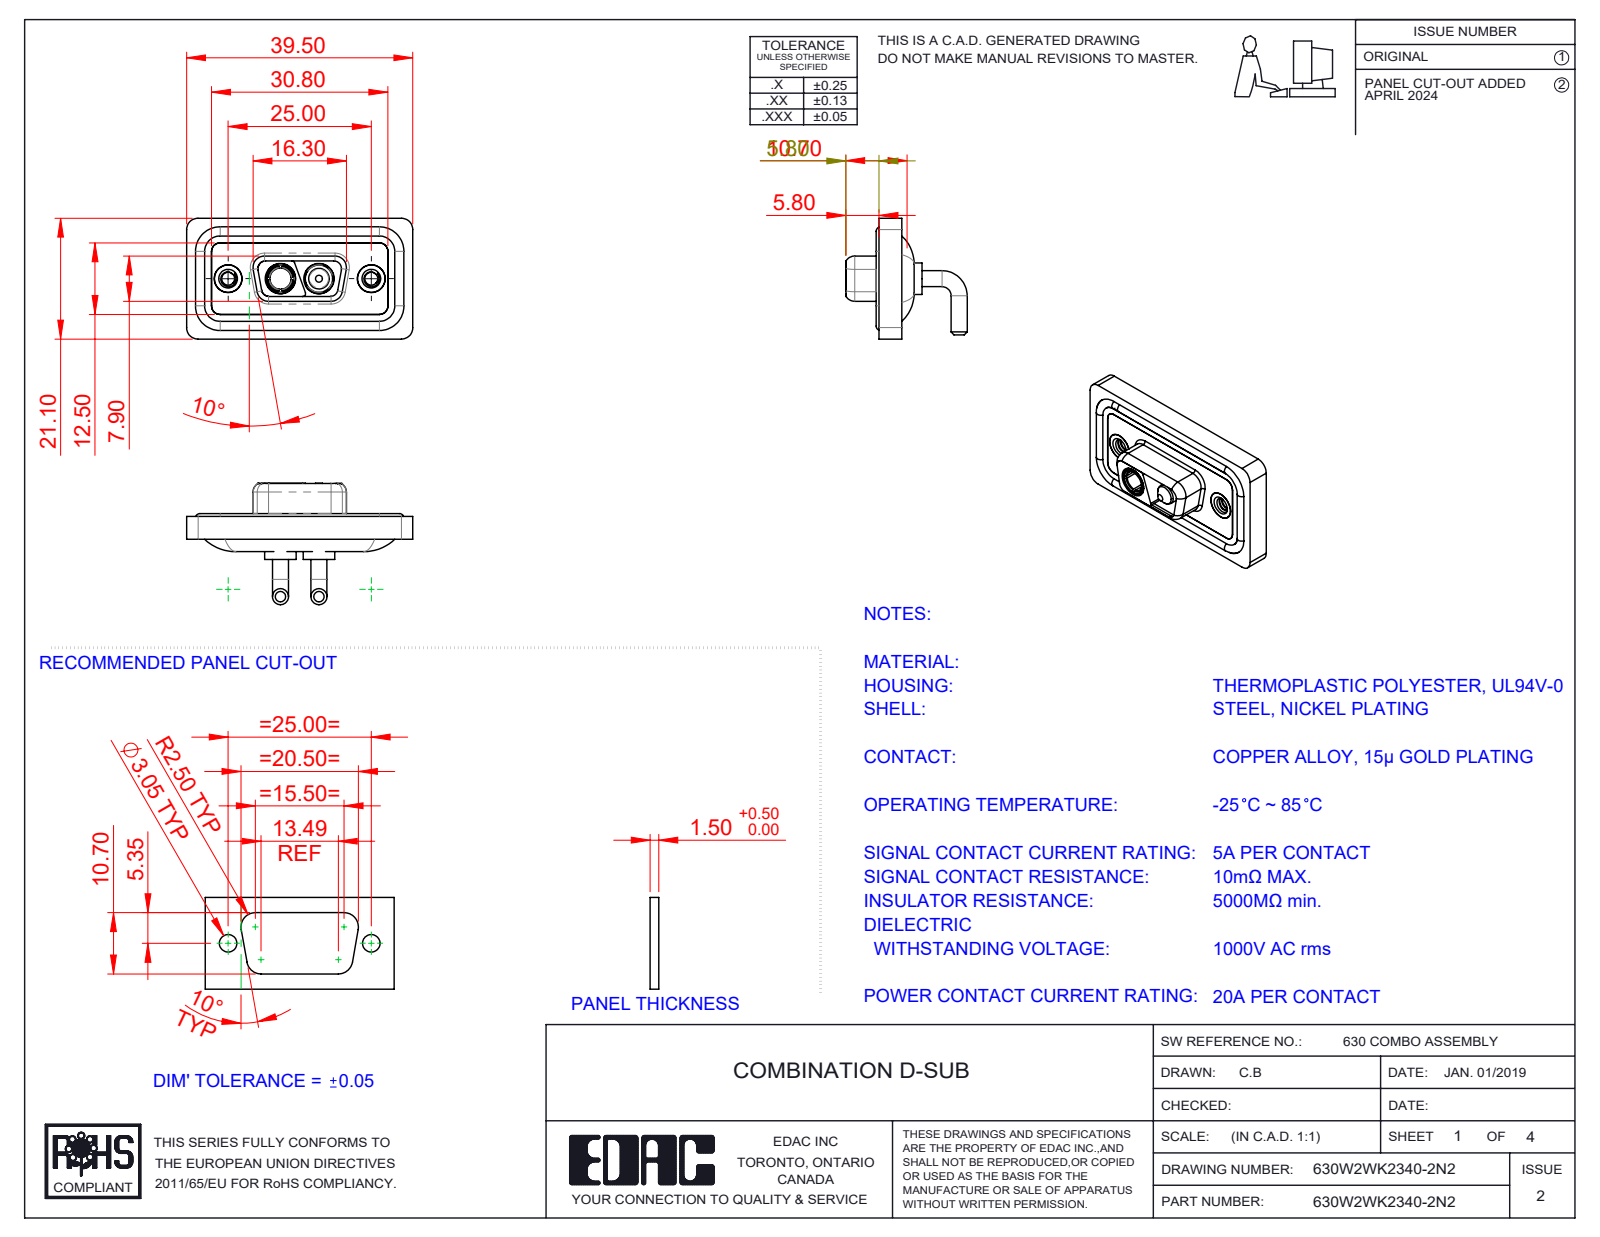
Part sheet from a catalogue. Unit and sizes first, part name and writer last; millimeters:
Units: millimetres
Overall size (bounding box): 39.5 × 21.2 × 21.1
Round holes (diameter × count): ⌀4.85 ×4, ⌀2.26 ×2, ⌀4 ×2, ⌀4.05 ×2, ⌀5 ×2, ⌀5.3 ×2, ⌀3.7 ×1
Round bosses / shafts (diameter × count): ⌀2.8 ×4, ⌀1.6 ×4, ⌀5.5 ×2, ⌀5.2 ×2, ⌀4.95 ×2, ⌀4.8 ×2, ⌀4.75 ×2, ⌀3.75 ×2
Partial cylindrical surfaces — rounded edges, fillets, slot ends (radius × count): R1.5 ×18, R2 ×18, R1.35 ×8, R1.6 ×8, R0.5 ×6, R0.25 ×4, R0.6 ×4, R0.65 ×4
Main face-to-face distances: 0.4, 1.1, 2.9, 1.8, 2.5, 1.6, 3.1, 1.5, 2.1, 3.7
Hole centre spacings: 9.14, 15.86, 6.72, 25
Volume: 4 706 mm³ · Surface area: 7 494 mm²
Bodies: 11 solids, 508 faces (144 planar, 235 cylindrical, 129 other)
Part name (STEP PRODUCT): 630Combo Threaded Rivet_2; 630Combo Housing_2WK2; Power Socket_20A RA; 630W2WK2340-2N2 (+4 more)
STEP written by: SolidWorks 2023 (CONFIG_CONTROL_DESIGN)
